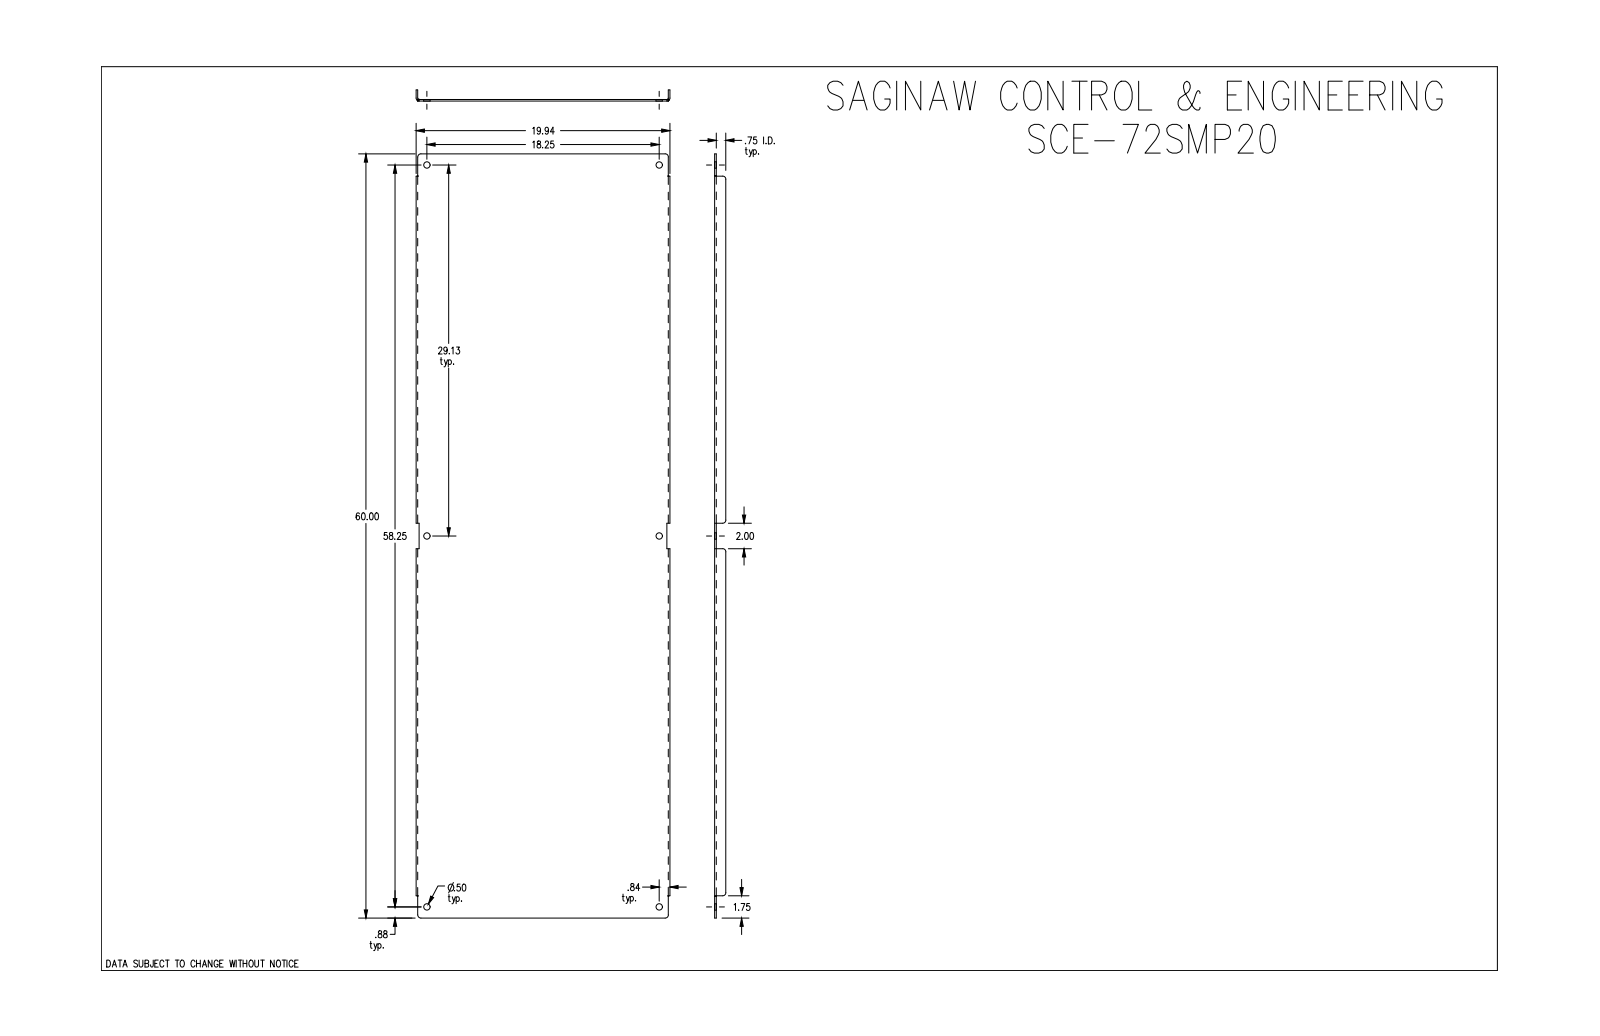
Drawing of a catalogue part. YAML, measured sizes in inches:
part_name: "SCE-72SMP20"
step_written_by: "SolidWorks 2019 (CONFIG_CONTROL_DESIGN)"
units: inches
bodies: {solids: 1, faces: 68, planar: 30, cylindrical: 26, other: 12}
overall_size: [60, 19.938, 0.875]
volume: 158.3
surface_area: 2555
round_holes:
  - {diameter: 0.5, count: 6}
partial_cylinders:
  - {radius: 0.25, count: 8}
  - {radius: 0.112, count: 2}
  - {radius: 0.237, count: 2}
face_to_face_distances: [0.125, 0.125, 19.813, 19.687, 19.938, 0.75, 0.875, 60, 0.237, 19.701]
hole_center_spacings: [29.125, 34.37, 18.25, 58.25, 61.041]
